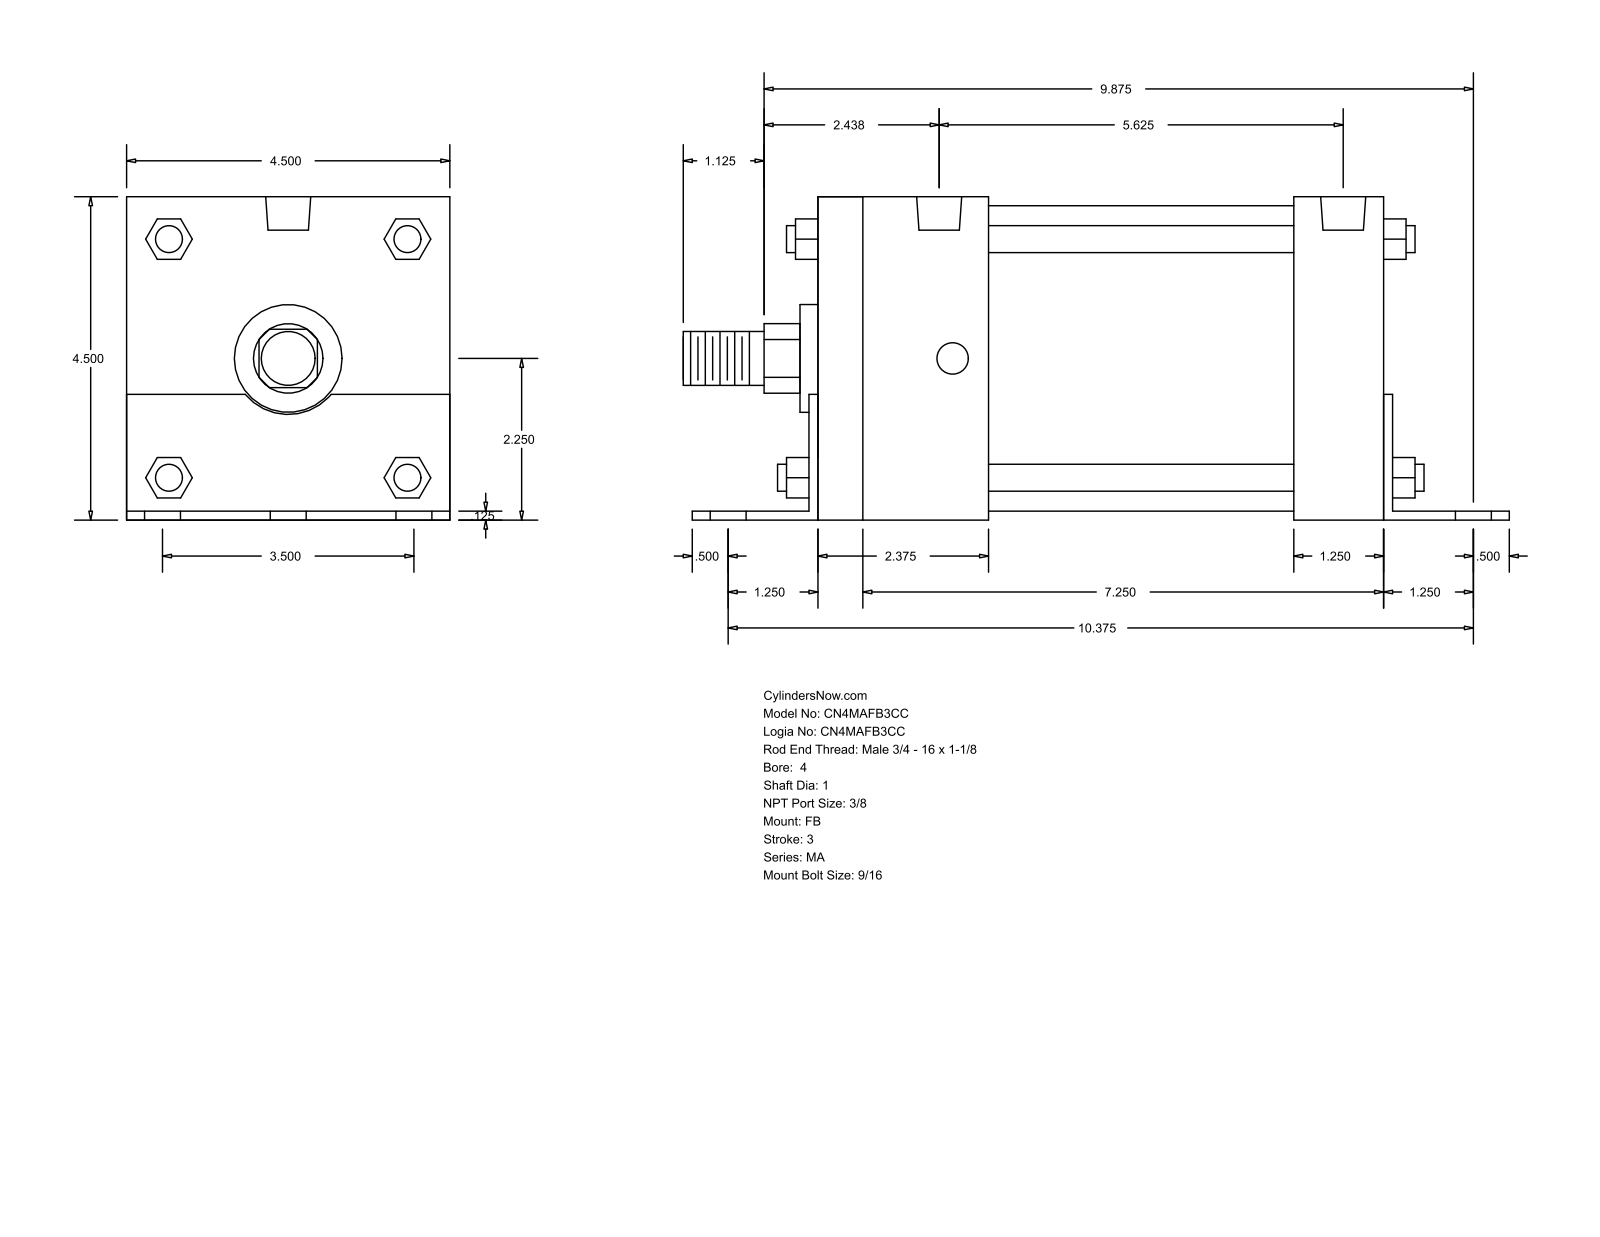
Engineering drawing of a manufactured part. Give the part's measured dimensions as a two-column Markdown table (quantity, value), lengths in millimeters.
| quantity | value |
| --- | --- |
| part name | MA_FB__0400_1 |
| STEP written by | GSSL Pune (CONFIG_CONTROL_DESIGN) |
| units | millimeters |
| bodies | 0 solids, 140 faces (105 planar, 35 cylindrical, 0 other) |
| overall size | 292.1 × 114.35 × 114.3 |
| round holes (diameter × count) | 14.29 × 6, 11.11 × 4, 15.93 × 2 |
| round bosses / shafts (diameter × count) | 9.53 × 4, 107.95 × 1, 38.1 × 1, 25.4 × 1, 19.05 × 1 |
| partial cylindrical surfaces (radius × count) | 12.29 × 1, 19.81 × 1 |
| main face-to-face distances | 114.3, 3.17, 114.35, 3.12, 111.18, 200.02, 3.18, 206.37, 203.2, 203.19 |
| hole center spacings | 44.45, 267.24, 263.52, 4.76, 63.99, 67.49, 86.85, 88.9 |
